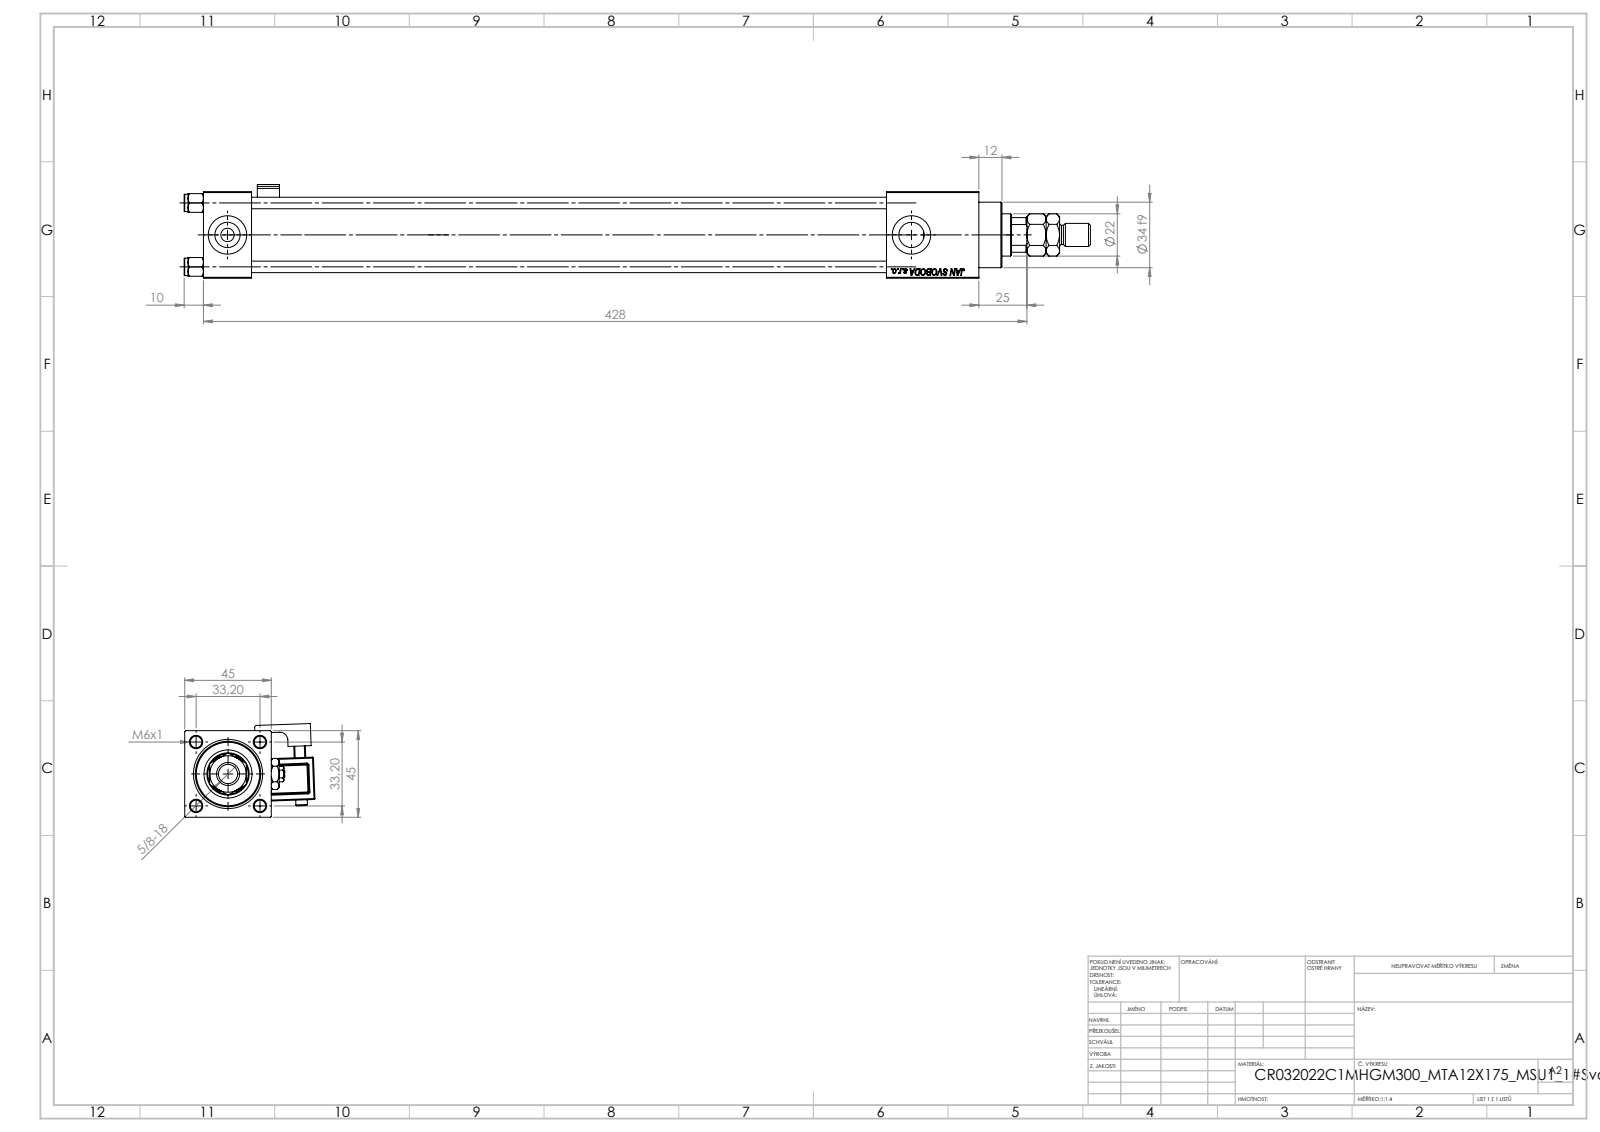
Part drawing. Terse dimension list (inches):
name: V215CR_C_Body; V215_VC_A; V215CR_VCP_C; MTA (+4 more)
written by: SolidWorks 2019 (CONFIG_CONTROL_DESIGN)
unit: in
bodies: 14 solids, 1323 faces (595 planar, 124 cylindrical, 604 other)
size: 18.543 × 2.663 × 1.918
volume: 28.49 in³; area: 282.8 in²
holes: 4× ⌀0.236, 2× ⌀0.276, 2× ⌀0.518, 2× ⌀0.787, 1× ⌀0.413, 1× ⌀0.866, 1× ⌀0.945, 1× ⌀0.984, 1× ⌀1.26, 1× ⌀1.299
bosses: 4× ⌀0.354, 1× ⌀1.496, 1× ⌀1.339, 1× ⌀0.472, 1× ⌀0.394, 1× ⌀0.236
rounds: 24× R0.02, 1× R0.039, 1× R0.098, 1× R0.157, 1× R0.413
face distances: 1.772, 0.984, 15.866, 0.118, 13.976, 12.992, 14.882, 0.512, 1.89, 14.736
hole spacings: 0.924, 1.307, 1.848, 13.996
